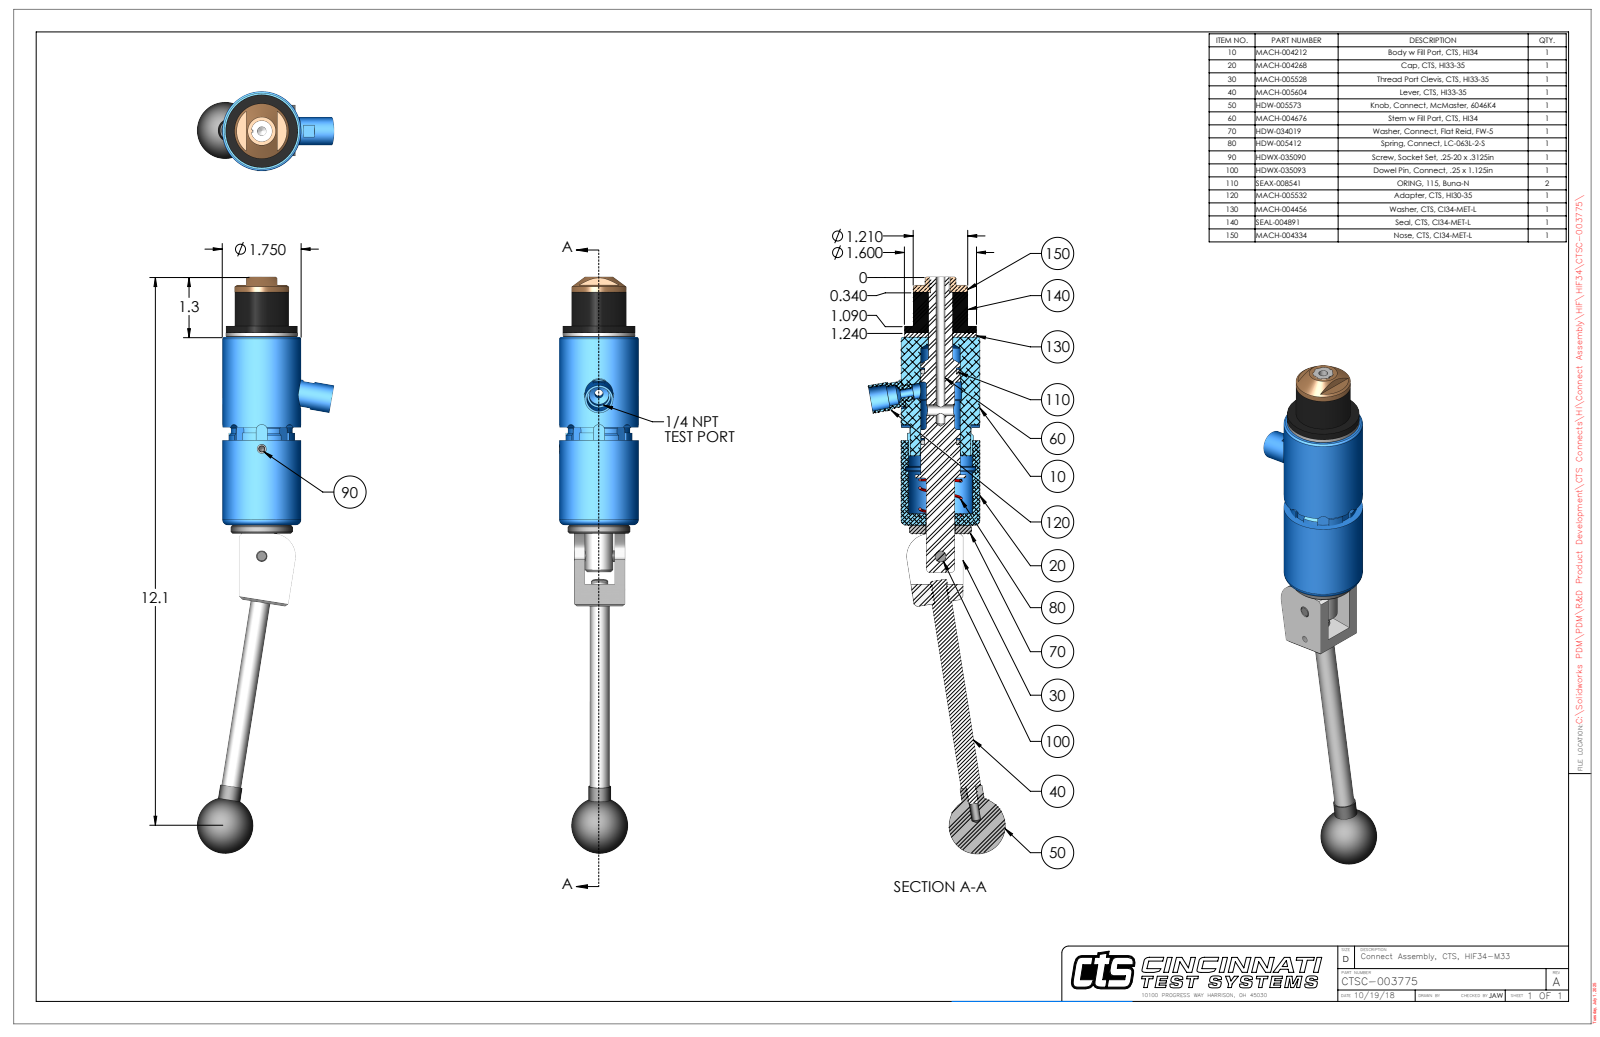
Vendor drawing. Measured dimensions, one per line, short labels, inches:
name: CTSC-003775
written by: SolidWorks 2023 (AUTOMOTIVE_DESIGN)
unit: in
bodies: 9 solids, 328 faces (120 planar, 139 cylindrical, 69 other)
size: 12.773 × 3.043 × 1.75
volume: 14.7 in³; area: 83.35 in²
holes: 2× ⌀0.201, 1× ⌀0.15, 1× ⌀0.187, 1× ⌀0.204, 1× ⌀0.249, 1× ⌀0.25, 1× ⌀0.251, 1× ⌀0.313, 1× ⌀0.422, 1× ⌀0.438, 1× ⌀0.53, 1× ⌀0.541
bosses: 2× ⌀0.5, 2× ⌀0.44, 2× ⌀0.25, 1× ⌀1.75, 1× ⌀1.6, 1× ⌀1.38, 1× ⌀1.21, 1× ⌀0.625
rounds: 4× R0.125, 2× R0.029, 1× R0.166, 1× R0.166, 1× R0.178, 1× R0.33, 1× R0.5, 1× R0.695
face distances: 0.094, 4.258, 4.164, 0.9, 0.994, 5.158, 1.12, 5.346, 4.446, 4.352
hole spacings: 0.74, 2.376, 3.116
